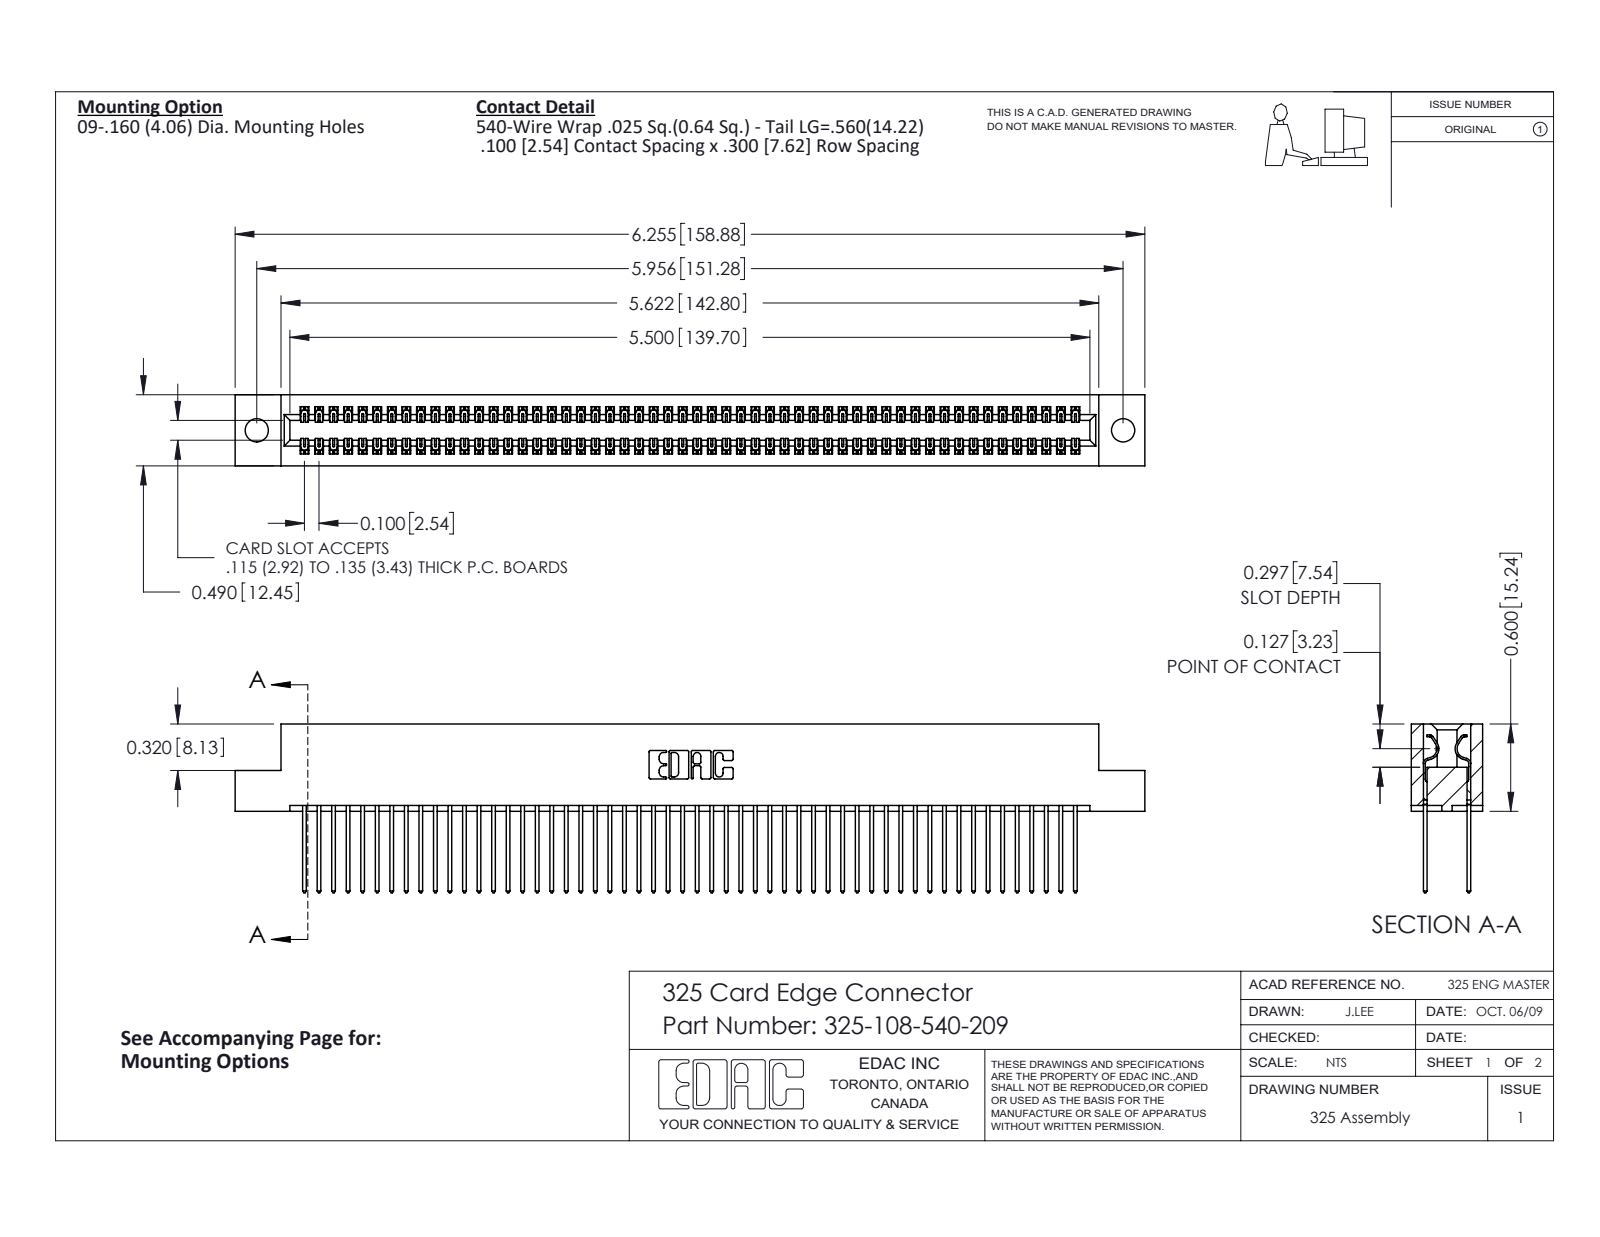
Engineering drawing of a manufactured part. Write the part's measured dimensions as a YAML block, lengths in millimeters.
part_name: "325-108-540-209; 325-292-001_325-293-140; 325 Part_.160 TH"
step_written_by: "SolidWorks 2016 (CONFIG_CONTROL_DESIGN)"
units: millimeters
bodies: {solids: 109, faces: 5730, planar: 3958, cylindrical: 1772, other: 0}
overall_size: [158.9, 29.5, 12.4]
volume: 20800
surface_area: 27320
round_holes:
  - {diameter: 4.1, count: 2}
partial_cylinders:
  - {radius: 0.2, count: 162}
  - {radius: 0.3, count: 108}
  - {radius: 0.3, count: 22}
  - {radius: 0.2, count: 6}
  - {radius: 0.8, count: 6}
  - {radius: 0.7, count: 3}
  - {radius: 0.4, count: 2}
  - {radius: 0.6, count: 2}
face_to_face_distances: [2.1, 10.3, 7.6, 2.7, 9.7, 0.6, 8.3, 12.4, 7, 14.2]
hole_center_spacings: [151.3]
